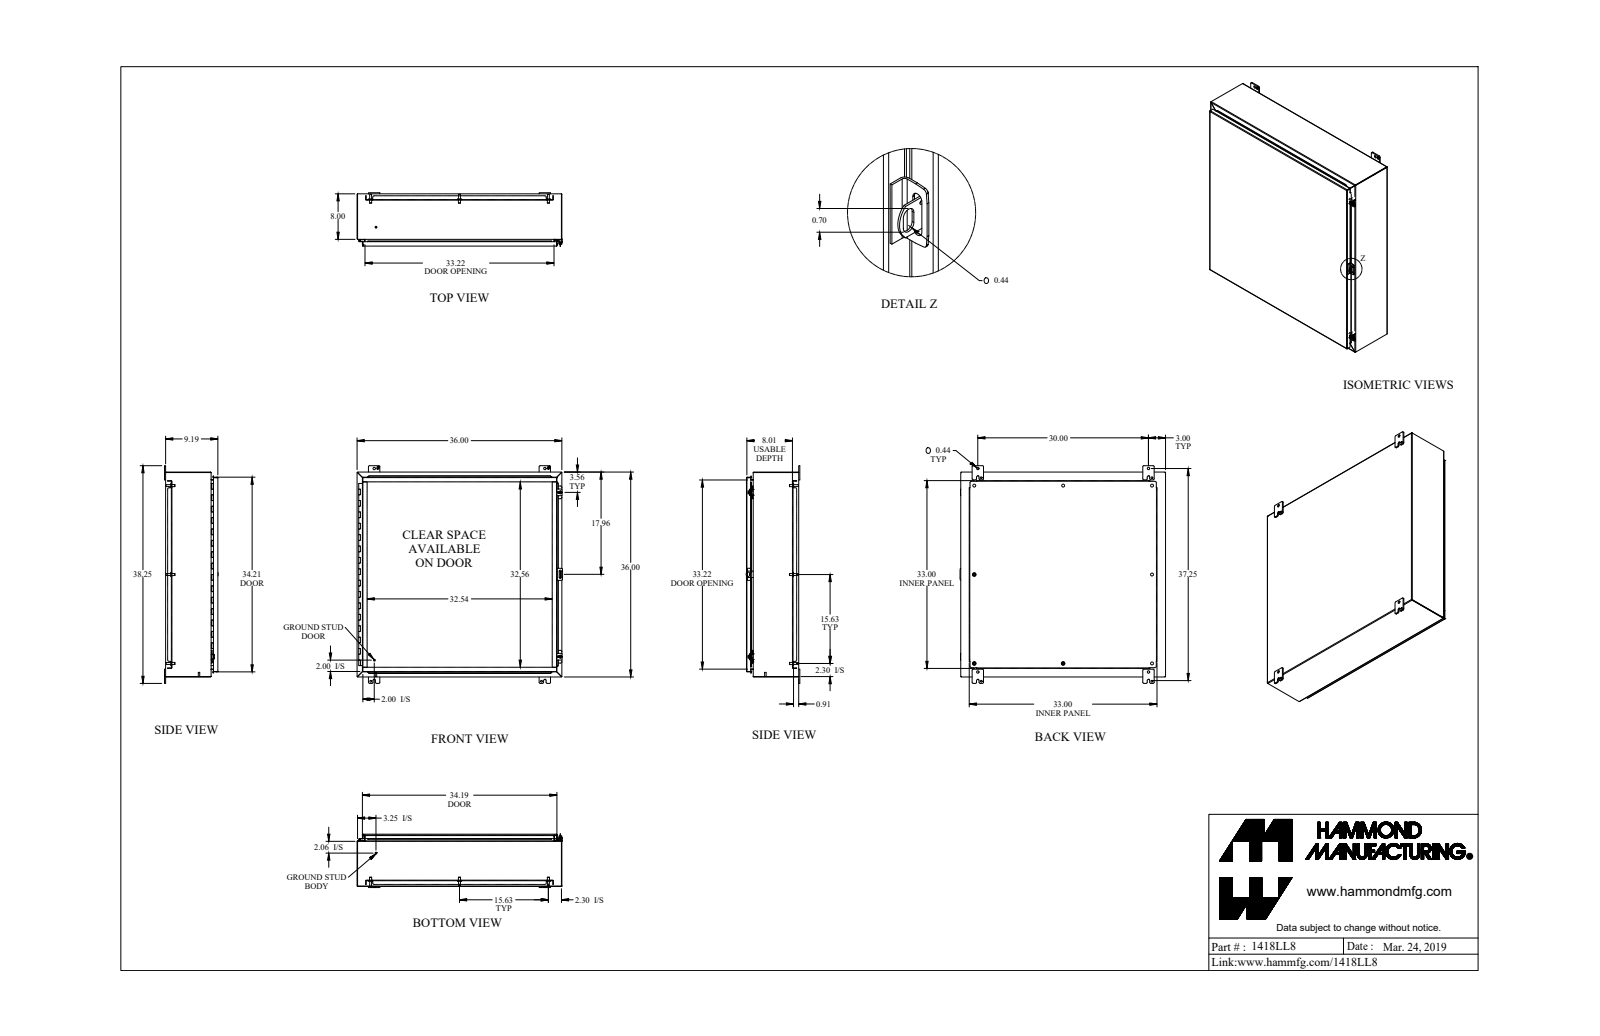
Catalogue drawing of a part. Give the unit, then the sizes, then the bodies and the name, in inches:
Units: inches
Overall size (bounding box): 38.25 × 36.125 × 9.437
Round holes (diameter × count): ⌀0.5 ×8, ⌀0.307 ×4, ⌀0.313 ×4, ⌀0.437 ×4, ⌀0.445 ×4, ⌀0.213 ×2, ⌀0.265 ×2, ⌀0.375 ×2, ⌀0.125 ×1, ⌀0.187 ×1
Round bosses / shafts (diameter × count): ⌀0.65 ×8, ⌀0.375 ×8, ⌀0.33 ×8, ⌀1 ×4, ⌀0.5 ×2, ⌀0.39 ×2, ⌀0.281 ×2, ⌀0.25 ×2
Partial cylindrical surfaces — rounded edges, fillets, slot ends (radius × count): R0.188 ×42, R0.036 ×24, R0.108 ×24, R0.116 ×16, R0.25 ×16, R0.048 ×13, R0.143 ×13, R0.045 ×8
Main face-to-face distances: 0.072, 9.113, 9.041, 9.185, 0.095, 0.937, 35.928, 1.009, 8.081, 8.009
Hole centre spacings: 15.625, 31.25, 34.939, 22.097, 30, 30.662, 34.939, 2.434
Volume: 458.9 in³ · Surface area: 11 868 in²
Bodies: 50 solids, 1499 faces (875 planar, 524 cylindrical, 100 other)
Part name (STEP PRODUCT): 1418LL8_Default
STEP written by: SolidWorks 2019 (CONFIG_CONTROL_DESIGN)
